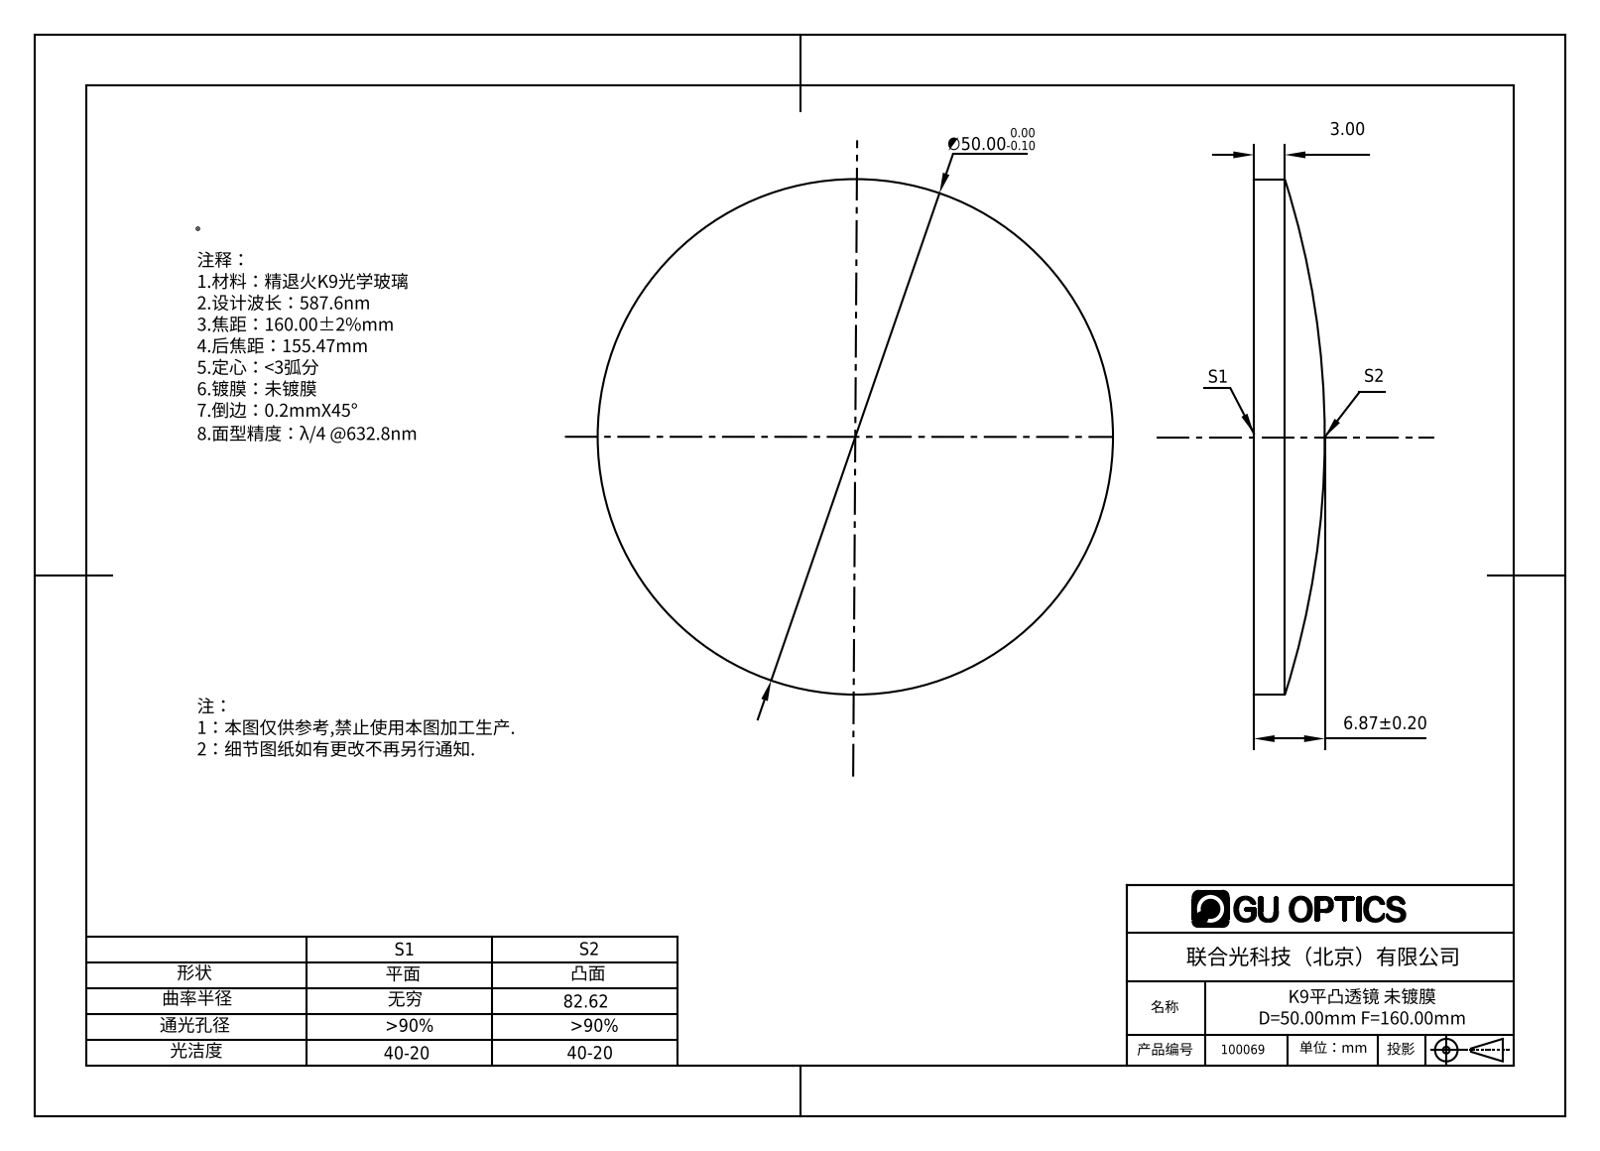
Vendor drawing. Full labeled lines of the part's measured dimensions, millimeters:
Part name (STEP PRODUCT): 100069
STEP written by: SolidWorks 2016 (AUTOMOTIVE_DESIGN)
Units: millimetres
Bodies: 1 solid, 5 faces (1 planar, 2 cylindrical, 2 other)
Overall size (bounding box): 50 × 50 × 6.87
Volume: 9 720 mm³ · Surface area: 4 445 mm²
Round bosses / shafts (diameter × count): ⌀50 ×1
